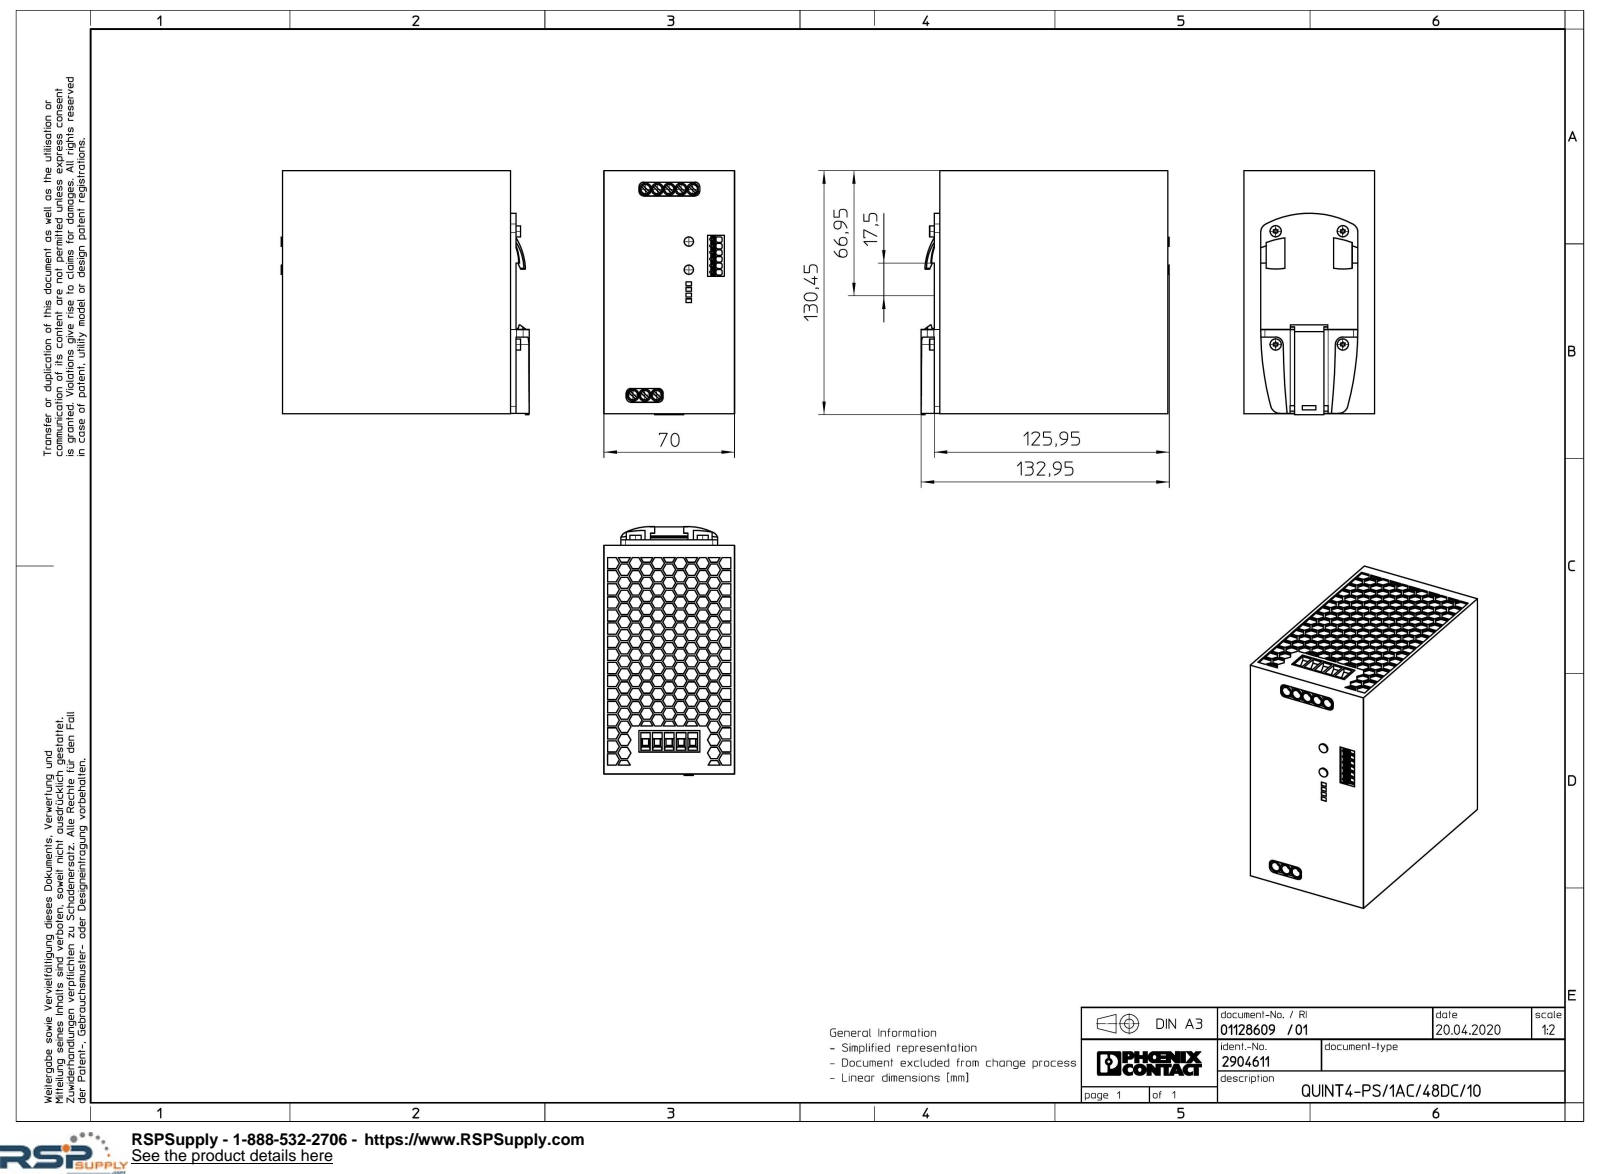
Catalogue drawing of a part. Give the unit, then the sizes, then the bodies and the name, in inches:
Units: inches
Overall size (bounding box): 5.234 × 5.136 × 2.756
Round holes (diameter × count): ⌀0.197 ×8
Round bosses / shafts (diameter × count): ⌀0.236 ×4, ⌀0.197 ×2
Partial cylindrical surfaces — rounded edges, fillets, slot ends (radius × count): R0.004 ×48, R0.038 ×12, R0.098 ×8, R0.128 ×8, R0.022 ×6, R0.024 ×6, R0.197 ×4, R0.157 ×2
Main face-to-face distances: 2.756, 0.031, 5.087, 5.055, 4.813, 0.118, 4.931, 5.118, 0.276, 0.272
Hole centre spacings: 0.25, 0.5, 0.75, 1
Volume: 68.71 in³ · Surface area: 122.3 in²
Bodies: 1 solid, 2840 faces (2683 planar, 139 cylindrical, 18 other)
Part name (STEP PRODUCT): QUINT4_PS_1AC_48DC_10-select
STEP written by: Creo Elements/Direct Modeling 20.1A 29-Sep-2018 (C) Parametric Technology GmbH (AUTOMOTIVE_DESIGN)
